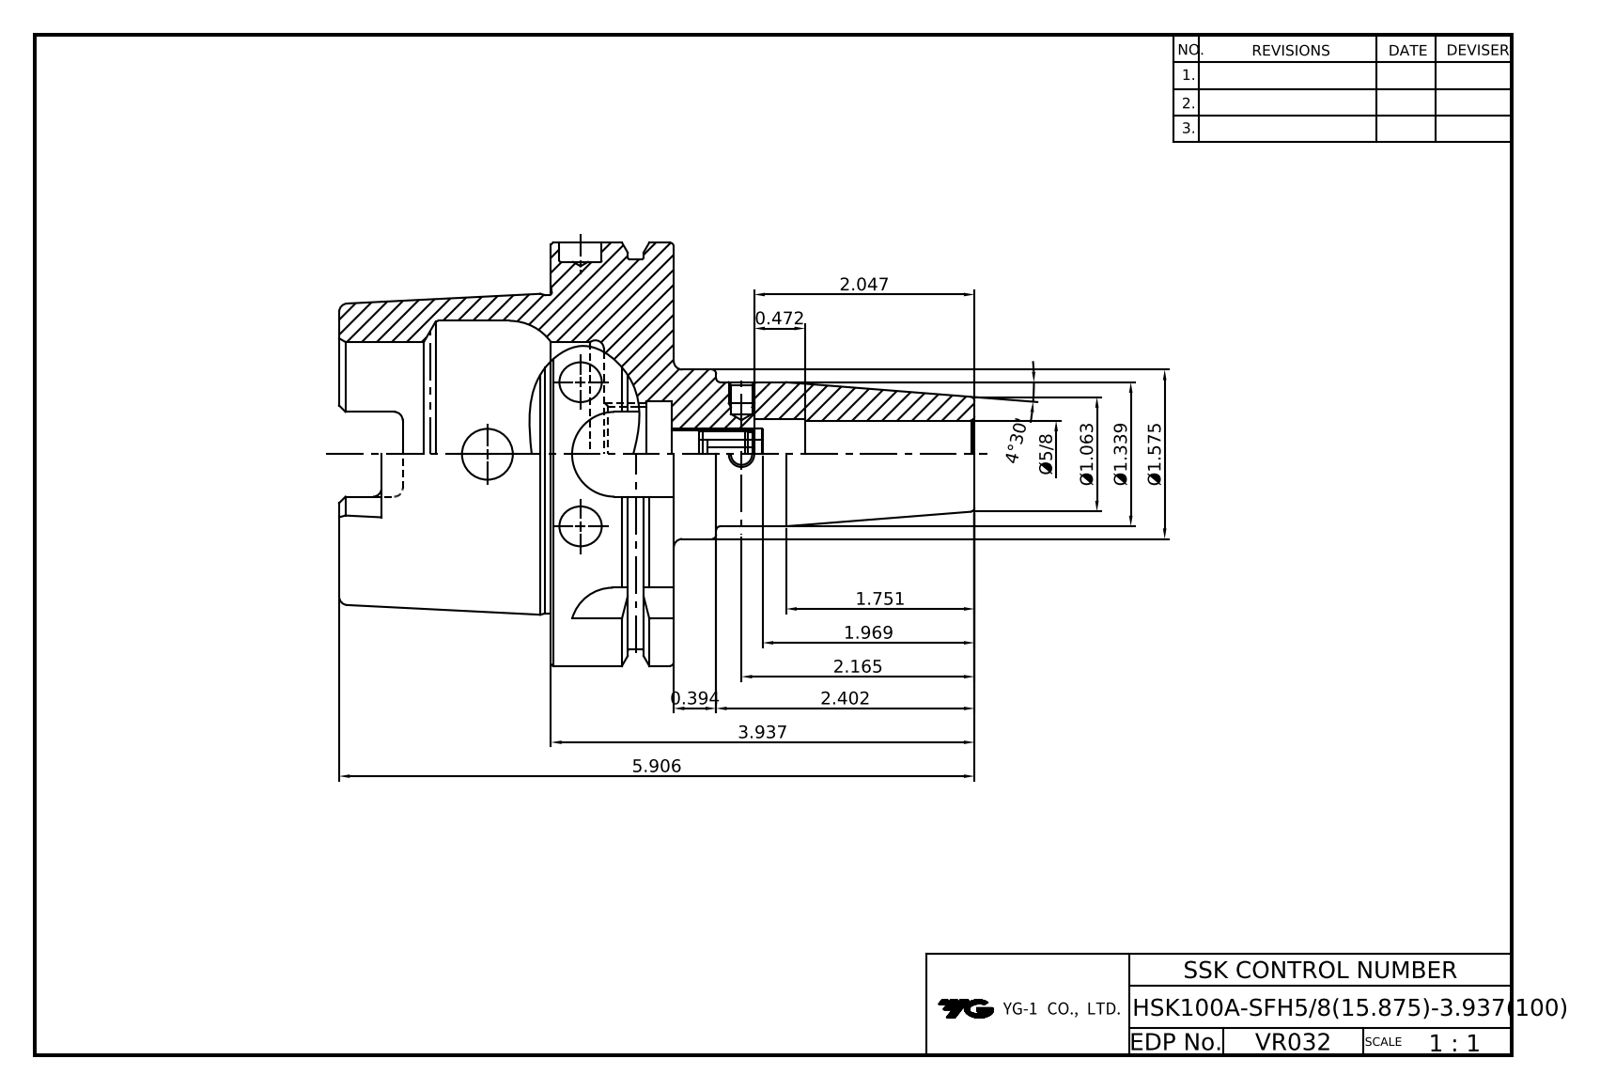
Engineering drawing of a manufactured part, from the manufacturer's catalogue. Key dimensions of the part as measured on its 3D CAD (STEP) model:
Part name (STEP PRODUCT): HSK100A_15_875_100
STEP written by: CREO PARAMETRIC BY PTC INC, 2018400 (CONFIG_CONTROL_DESIGN)
Units: millimetres
Bodies: 1 solid, 213 faces (57 planar, 70 cylindrical, 86 other)
Overall size (bounding box): 150 × 100 × 100
Volume: 298 639 mm³ · Surface area: 61 867 mm²
Round holes (diameter × count): ⌀5 ×2, ⌀6 ×2, ⌀10 ×1, ⌀11 ×1, ⌀11.1 ×1, ⌀12 ×1, ⌀15.87 ×1, ⌀16.47 ×1, ⌀22.5 ×1, ⌀24 ×1, ⌀25 ×1, ⌀53 ×1
Round bosses / shafts (diameter × count): ⌀100 ×1, ⌀92 ×1, ⌀75.16 ×1, ⌀40 ×1, ⌀34 ×1
Partial cylindrical surfaces — rounded edges, fillets, slot ends (radius × count): R2 ×6, R4.88 ×4, R10 ×4
Main face-to-face distances: 29, 12.5, 16.5, 62.5, 79, 50, 10, 72.5, 22.5, 6.5
Hole centre spacings: 38, 60
